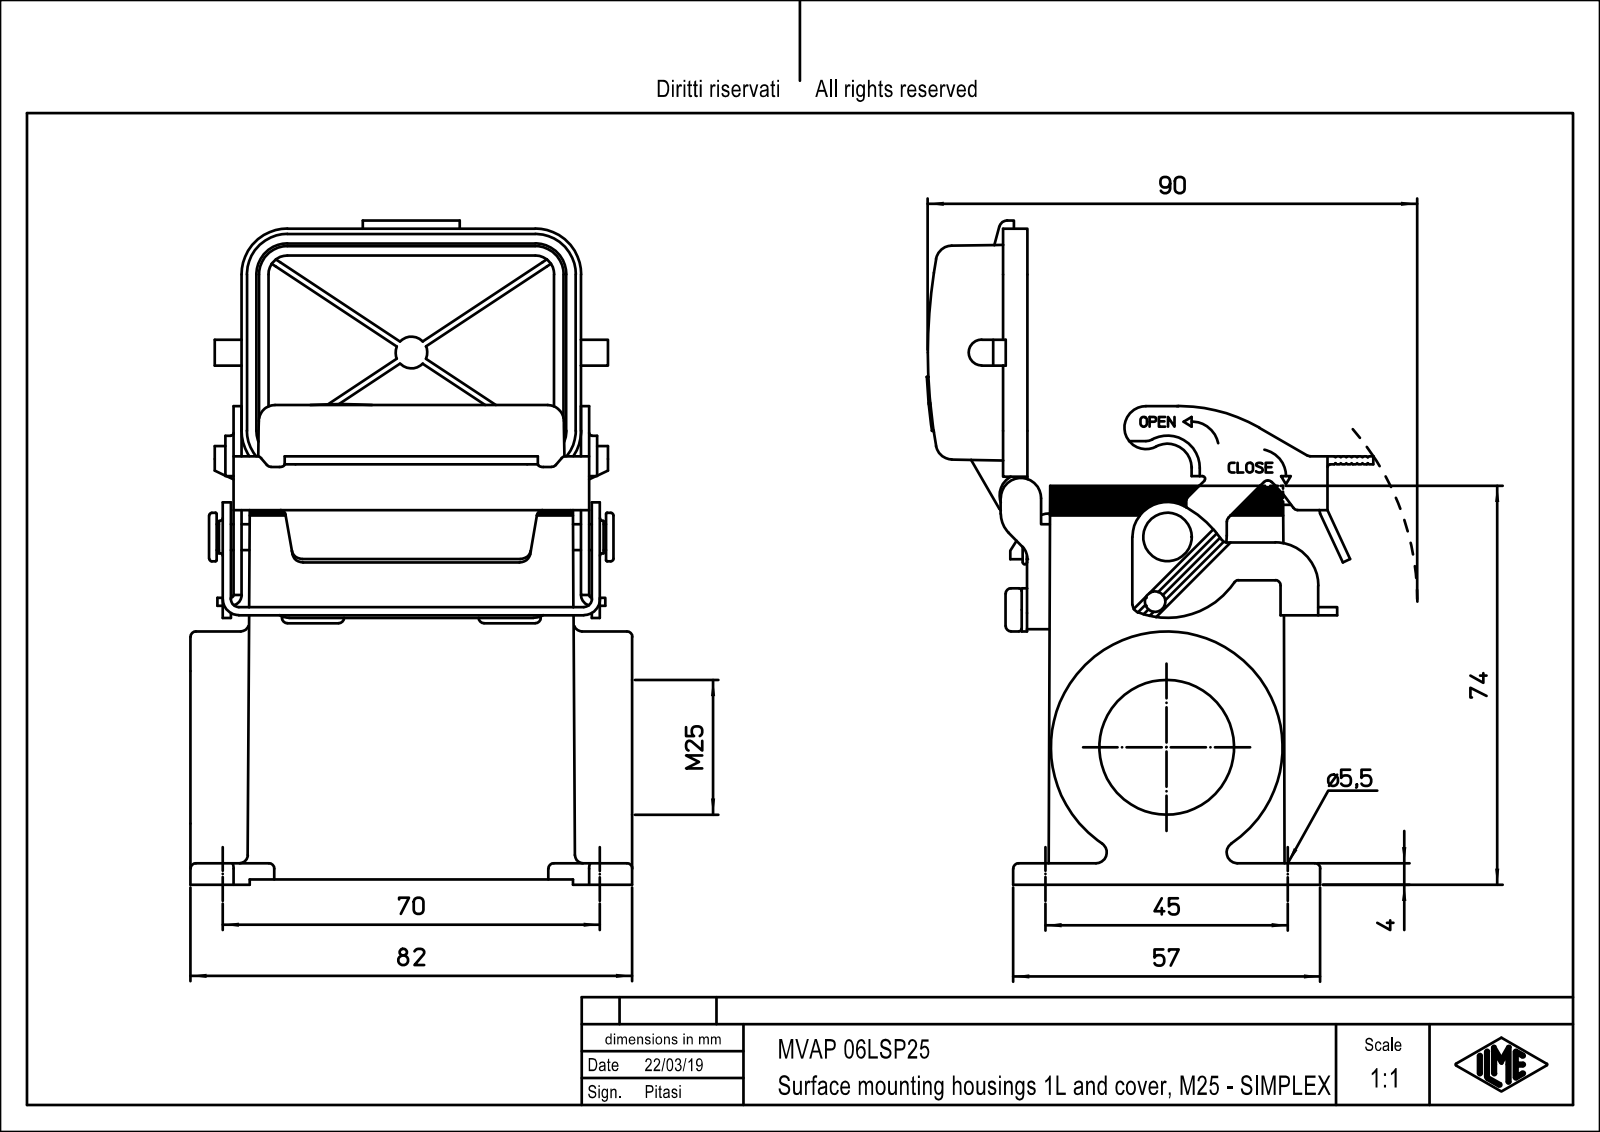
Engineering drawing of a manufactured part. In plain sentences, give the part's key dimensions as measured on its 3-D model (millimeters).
The part is named "MVAP_06_LSP25; MVAP_06LSP25.stp". Its 3-D file was written by "PTC Creo Elements/Direct Modeling 19.0E 27-Jun-2016 (C) Parametric Technology GmbH (AUTOMOTIVE_DESIGN)". It is 1 solid with 608 faces: 383 planar, 201 cylindrical and 24 other. Overall it measures 122.72 by 82 by 79.9 millimeters. Its volume is 130 038 cubic millimeters and its surface area 62 161 square millimeters. Round holes: 4 of diameter 2.46, 4 of diameter 3, 4 of diameter 5.5, 1 of diameter 20, 1 of diameter 25. Round bosses or shafts: 3 of diameter 0.8, 1 of diameter 43, 1 of diameter 9, 1 of diameter 8.4, 1 of diameter 8, 1 of diameter 6, 1 of diameter 2.4. Partial cylindrical surfaces (rounded edges, fillets, slot ends): 20 of radius 2, 15 of radius 3, 8 of radius 1.5, 7 of radius 3.5, 5 of radius 1, 5 of radius 6, 4 of radius 0.5, 4 of radius 1.8. The main face-to-face distances are 4, 40.5, 59.5, 44.5, 1.5, 36.5, 2, 47.75, 22.5, 8. The hole center spacings are 15.81, 38.28, 57.71, 67.42, 27, 44, 45, 51.62.
